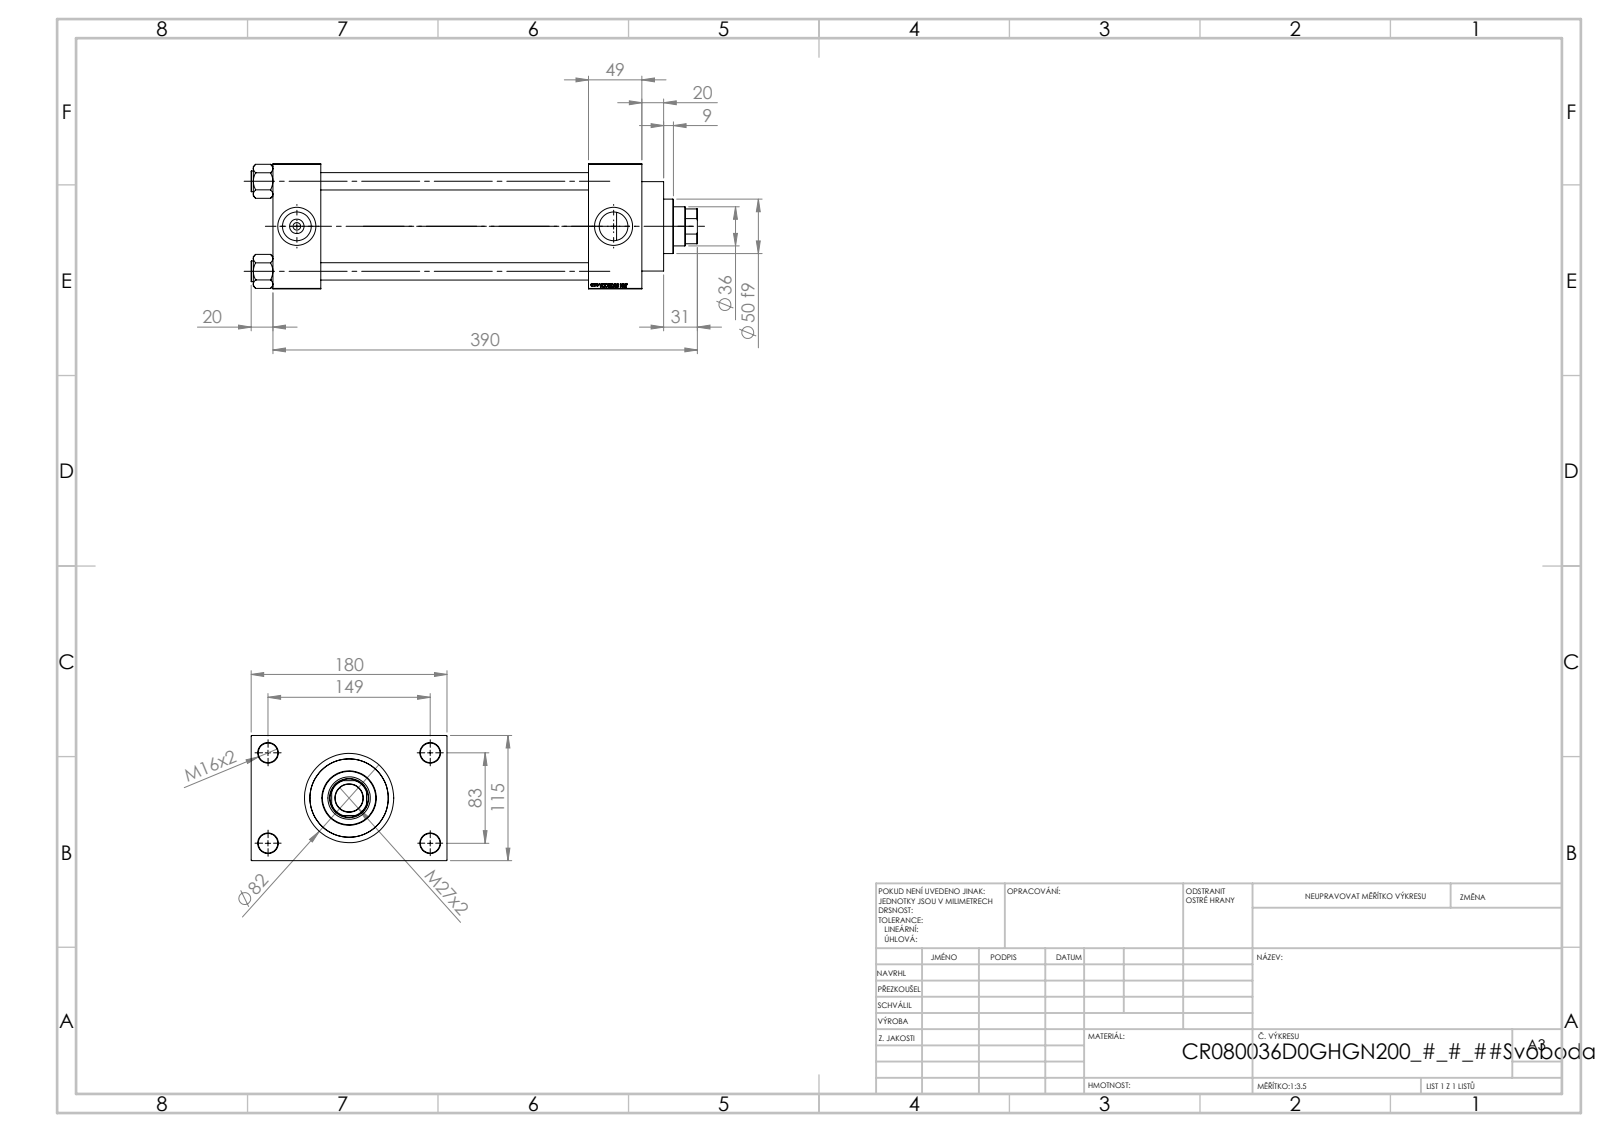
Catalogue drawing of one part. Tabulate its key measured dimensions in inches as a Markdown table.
| quantity | value |
| --- | --- |
| part name | NUT_M5_D; V215CR_D_Body; V215_VC_A; V215CR_D_TYCINKA (+1 more) |
| STEP written by | SolidWorks 2019 (CONFIG_CONTROL_DESIGN) |
| units | inches |
| bodies | 11 solids, 1151 faces (545 planar, 88 cylindrical, 518 other) |
| overall size | 16.142 × 7.087 × 4.528 |
| volume | 149.4 in³ |
| surface area | 692.9 in² |
| round holes (diameter × count) | 0.63 × 4, 0.709 × 4, 0.276 × 2, 1.041 × 2, 1.378 × 2, 1.004 × 1, 1.417 × 1, 1.535 × 1, 2.402 × 1, 2.835 × 1, 3.15 × 1 |
| round bosses / shafts (diameter × count) | 0.748 × 4, 3.386 × 1, 3.228 × 1, 1.969 × 1 |
| partial cylindrical surfaces (radius × count) | 0.689 × 1 |
| main face-to-face distances | 4.528, 9.685, 11.614, 1.929, 1.732, 11.417, 13.346, 1.28, 5.807, 7.087 |
| hole center spacings | 1.305, 2.302, 3.256, 3.357, 3.513, 4.561, 5.607, 3.268 |
